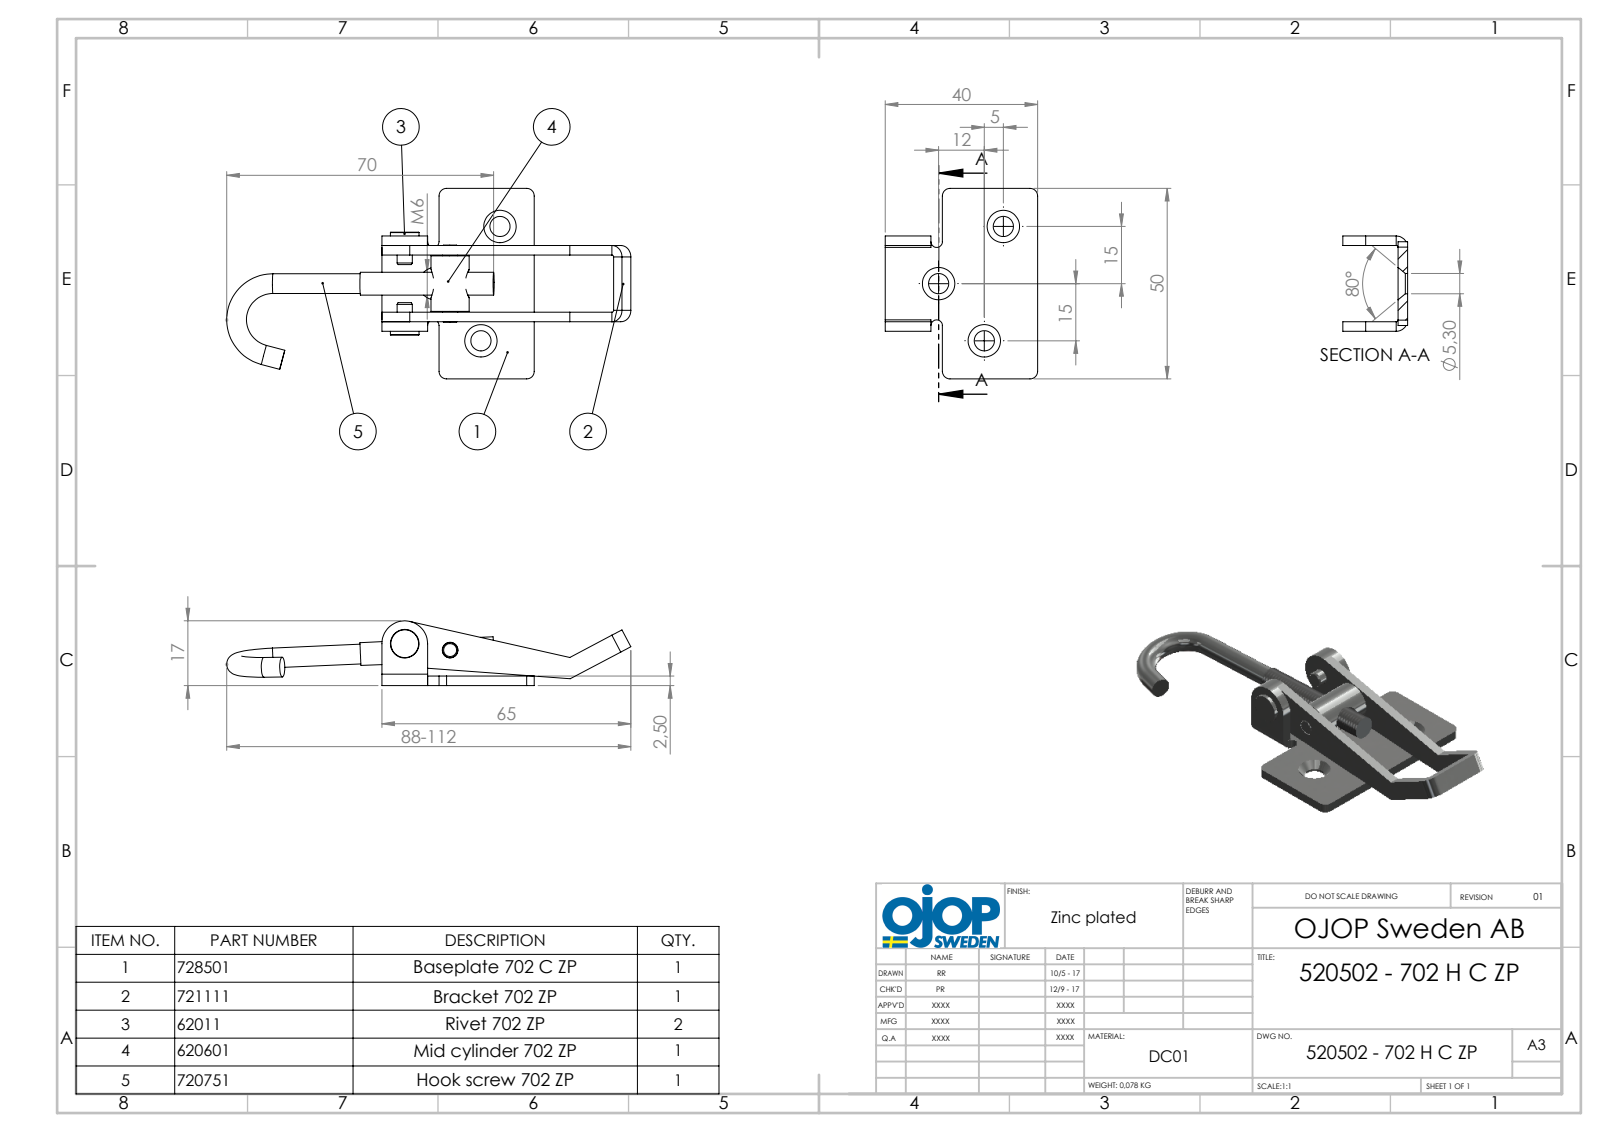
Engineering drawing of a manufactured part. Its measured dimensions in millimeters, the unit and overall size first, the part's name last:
Units: millimetres
Overall size (bounding box): 105.82 × 50 × 17.55
Round holes (diameter × count): ⌀5.3 ×3, ⌀4.1 ×2, ⌀5 ×1, ⌀6 ×1
Round bosses / shafts (diameter × count): ⌀5.18 ×2, ⌀4 ×2, ⌀10 ×1, ⌀7.5 ×1, ⌀6 ×1
Partial cylindrical surfaces — rounded edges, fillets, slot ends (radius × count): R0.5 ×4, R2 ×4, R3 ×4, R1.5 ×2, R6 ×1
Main face-to-face distances: 2.5, 17.5, 20, 15, 5, 22.5, 25, 19.8, 5.2, 2.7
Hole centre spacings: 12.03, 19.21, 22.67, 30.41
Volume: 10 563 mm³ · Surface area: 10 195 mm²
Bodies: 6 solids, 144 faces (57 planar, 63 cylindrical, 24 other)
Part name (STEP PRODUCT): 702 - C; 702 - Hake M6; 520502 - 702 H C ZP; 702 - Bygel (+2 more)
STEP written by: SolidWorks 2015 (AUTOMOTIVE_DESIGN)
